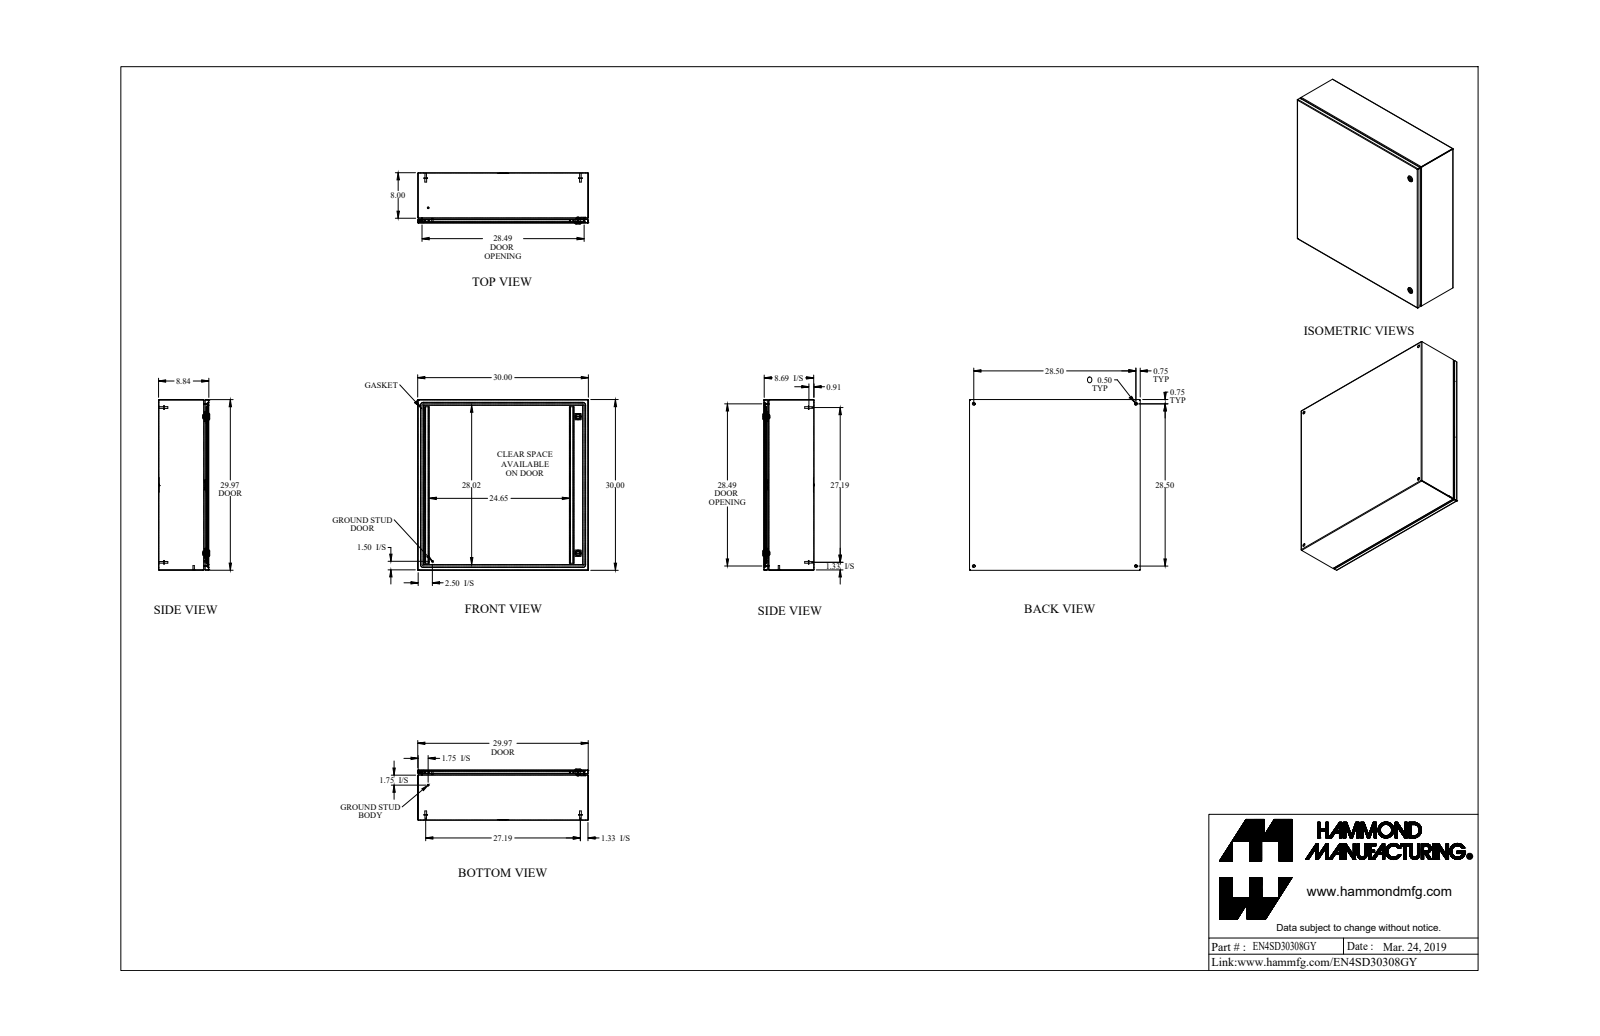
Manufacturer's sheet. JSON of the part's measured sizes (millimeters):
{"part_name": "EN4SD30308GY_Default", "step_written_by": "SolidWorks 2019 (CONFIG_CONTROL_DESIGN)", "units": "millimeters", "bodies": {"solids": 29, "faces": 866, "planar": 420, "cylindrical": 286, "other": 160}, "overall_size": [762, 762, 228.5], "volume_mm3": 3784000, "surface_area_mm2": 4172000, "round_holes": [[12.7, 4], [5.9, 2], [15.9, 2], [19.9, 2], [4.4, 1], [6.1, 1], [6.1, 1]], "round_bosses_or_shafts": [[15.9, 4], [8, 4], [6.9, 4], [27.9, 2], [13.3, 2], [7.1, 2], [6.4, 2], [11.6, 1]], "partial_cylinders_radius": [[0.9, 20], [2.7, 20], [1.1, 12], [2.1, 12], [9.7, 12], [482.7, 8], [0.2, 6], [1.6, 6]], "face_to_face_distances": [1.8, 222.6, 760.2, 220.8, 224.5, 758.3, 762, 21.3, 201.4, 19.1], "hole_center_spacings": [723.9, 63.3, 667.3, 699, 964.3, 1023.7, 609.6]}
